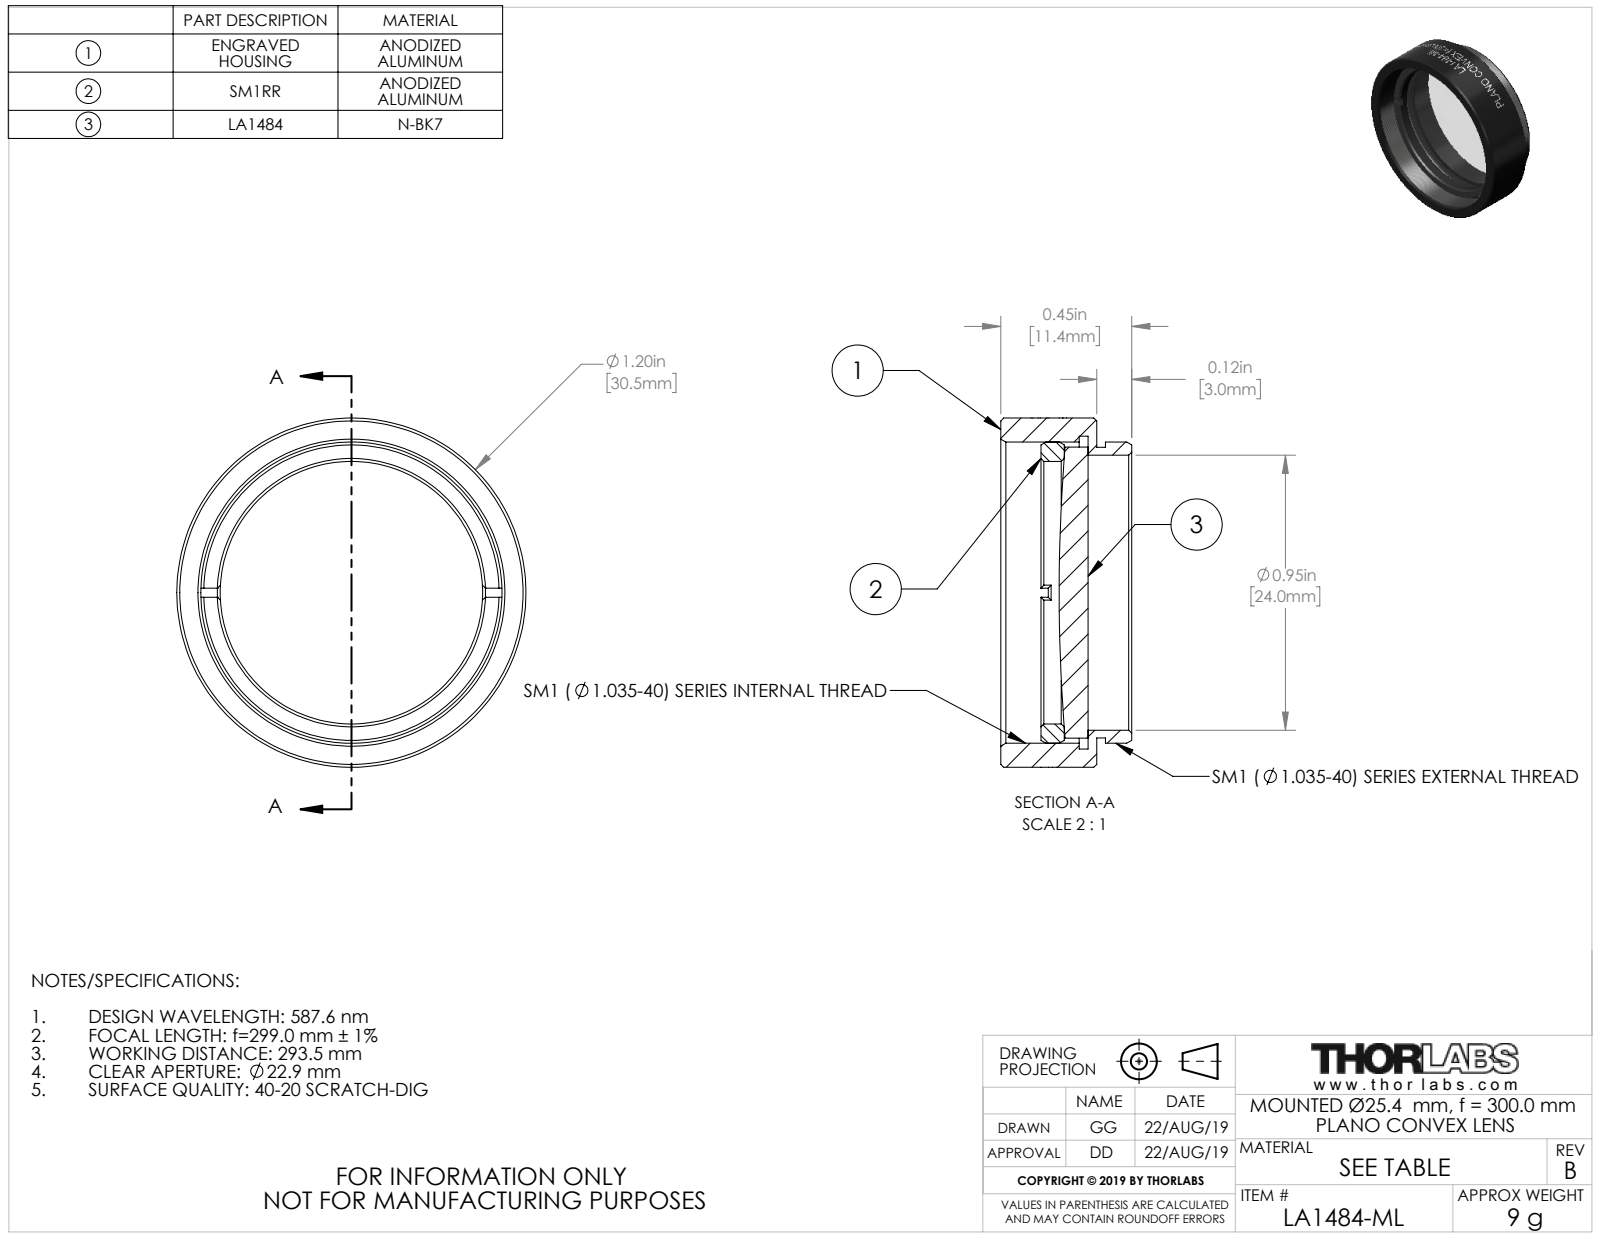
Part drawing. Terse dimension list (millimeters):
name: 24422-E0W
written by: SolidWorks 2018 (CONFIG_CONTROL_DESIGN)
unit: mm
bodies: 3 solids, 121 faces (20 planar, 77 cylindrical, 24 other)
size: 30.48 × 30.48 × 11.43
volume: 3 226 mm³; area: 4 313 mm²
holes: 1× ⌀22.91, 1× ⌀24, 1× ⌀26.29, 1× ⌀27.3
bosses: 1× ⌀30.48, 1× ⌀26.29, 1× ⌀25.4, 1× ⌀25.37
face distances: 0.76, 8.38, 7.62, 2.84, 2.08, 5.54, 4.87, 4.11, 2.03, 3.51
